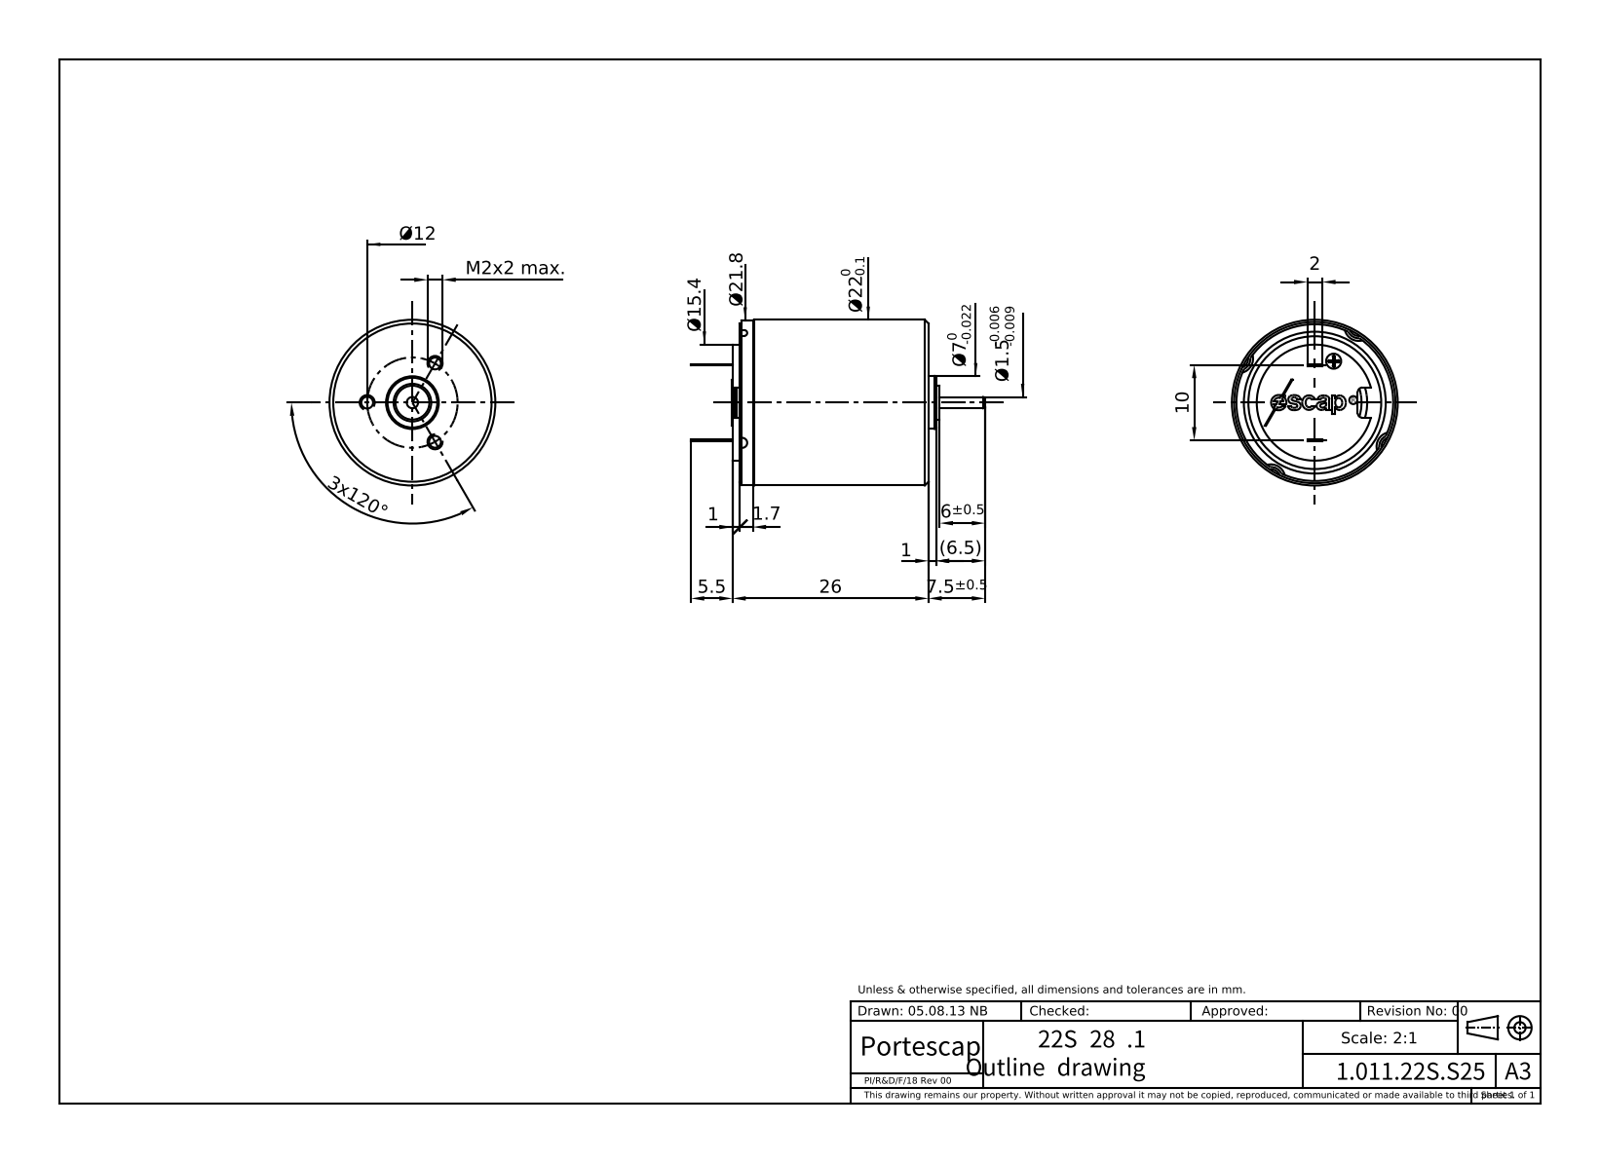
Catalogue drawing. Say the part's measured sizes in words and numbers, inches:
The part is named "22S_28". Its 3-D file was written by "PRO/ENGINEER BY PARAMETRIC TECHNOLOGY CORPORATION, 2014310 (CONFIG_CONTROL_DESIGN)". It is 1 solid with 369 faces: 179 planar, 117 cylindrical and 73 other. Overall it measures 1.535 by 0.868 by 0.868 inches. Its volume is 0.582 cubic inches and its surface area 5.656 square inches. Round holes: 7 of diameter 0.063, 3 of diameter 0.079, 2 of diameter 0.098, 1 of diameter 0.059, 1 of diameter 0.06, 1 of diameter 0.087, 1 of diameter 0.197, 1 of diameter 0.606, 1 of diameter 0.827, 1 of diameter 0.835. Round bosses or shafts: 1 of diameter 0.866, 1 of diameter 0.858, 1 of diameter 0.823, 1 of diameter 0.425, 1 of diameter 0.276, 1 of diameter 0.177, 1 of diameter 0.166, 1 of diameter 0.142. Partial cylindrical surfaces (rounded edges, fillets, slot ends): 13 of radius 0.02, 4 of radius 0.008, 4 of radius 0.016, 4 of radius 0.024, 4 of radius 0.039, 4 of radius 0.055, 2 of radius 0.069, 1 of radius 0.028. The main face-to-face distances are 1.024, 0.02, 0.961, 0.063, 0.039, 0.028, 0.043, 1.004, 0.024, 0.984. The hole center spacings are 0.195, 0.236, 0.104, 0.133, 0.22, 0.295, 0.318, 0.323.
